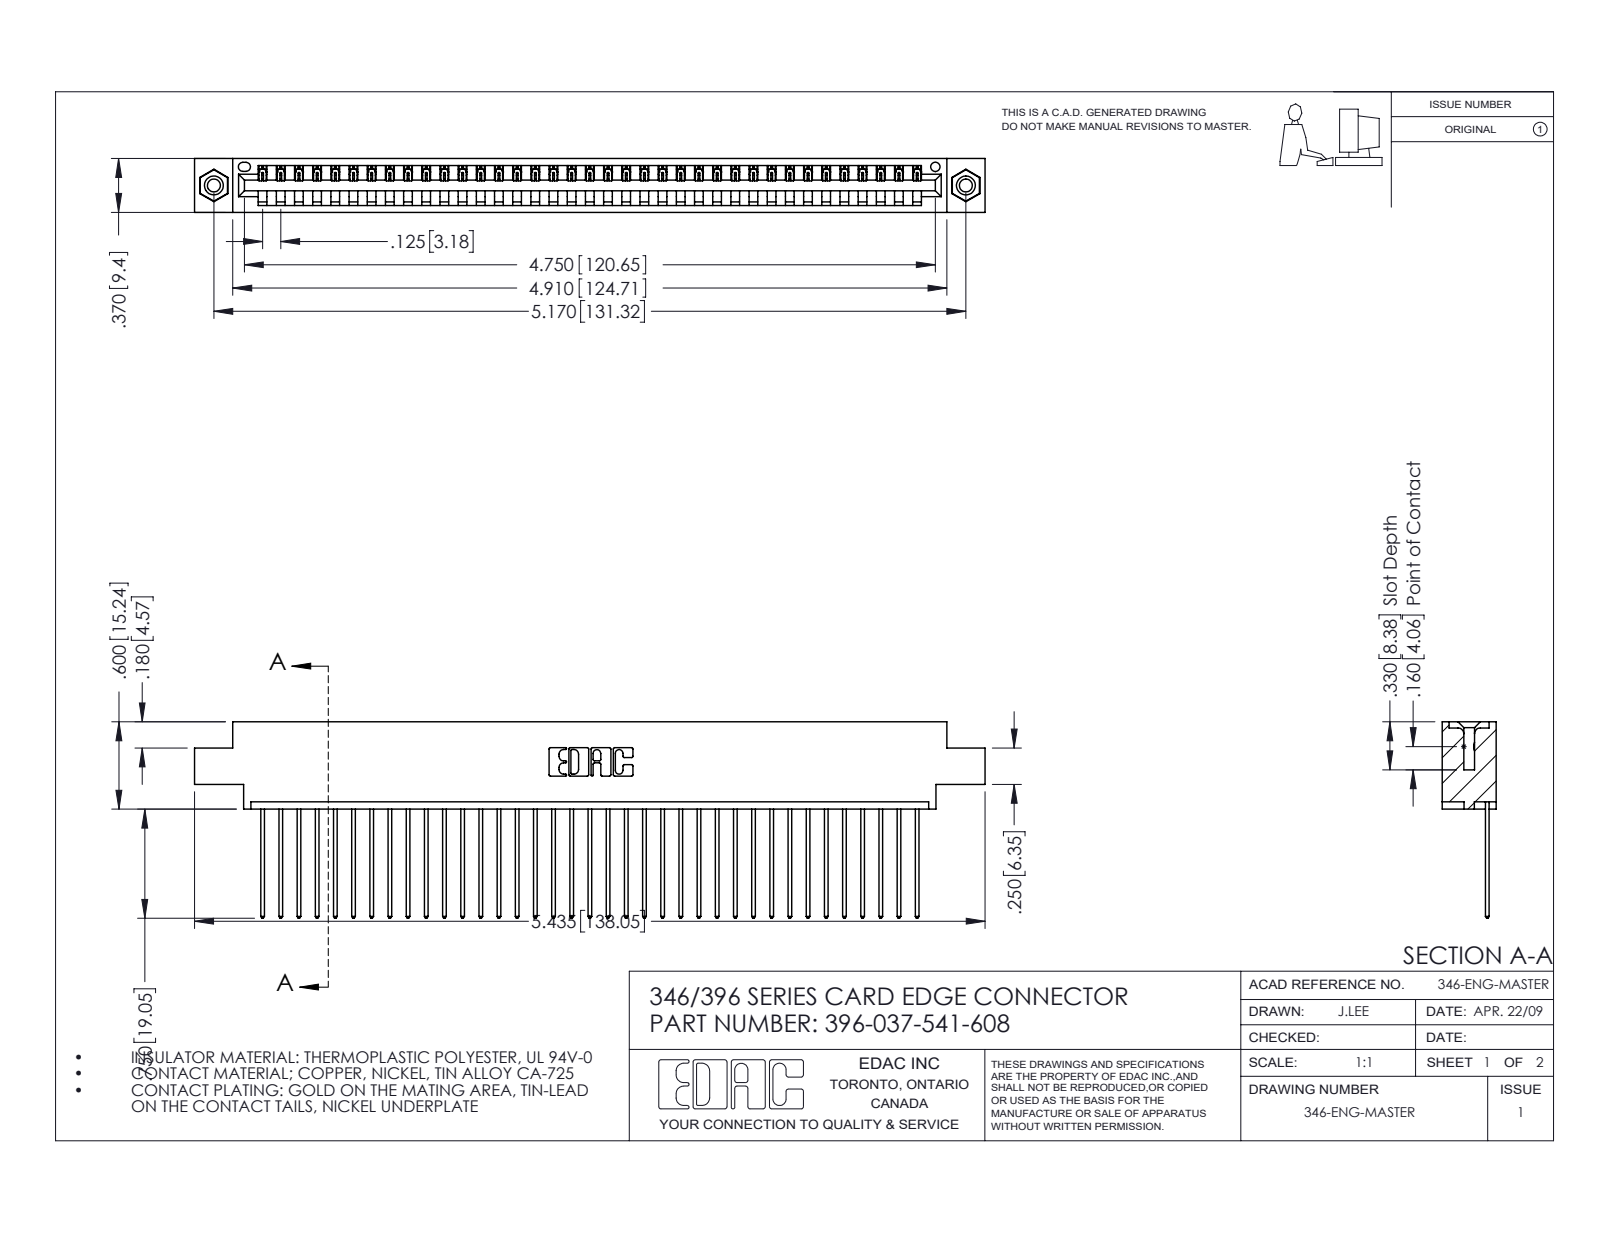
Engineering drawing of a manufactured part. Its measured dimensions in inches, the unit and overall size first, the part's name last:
Units: inches
Overall size (bounding box): 5.435 × 1.35 × 0.37
Round holes (diameter × count): ⌀0.089 ×2, ⌀0.125 ×2, ⌀0.156 ×2, ⌀0.064 ×1
Round bosses / shafts (diameter × count): ⌀0.155 ×2
Partial cylindrical surfaces — rounded edges, fillets, slot ends (radius × count): R0.006 ×74, R0.01 ×74, R0.01 ×22, R0.007 ×6, R0.031 ×6, R0.026 ×3, R0.031 ×2, R0.04 ×2
Main face-to-face distances: 0.048, 0.322, 0.37, 0.25, 0.072, 0.298, 0.025, 0.222, 0.148, 0.1
Hole centre spacings: 0.246, 4.961, 5.17
Volume: 0.802 in³ · Surface area: 26.79 in²
Bodies: 40 solids, 2332 faces (1592 planar, 724 cylindrical, 16 other)
Part name (STEP PRODUCT): 345-250-001_345-250-003-102; 346 Part_0.170 Offset - 0.156 Dia-TI; 345-292-001_345-293-141; 396-037-541-608
STEP written by: SolidWorks 2016 (CONFIG_CONTROL_DESIGN)
